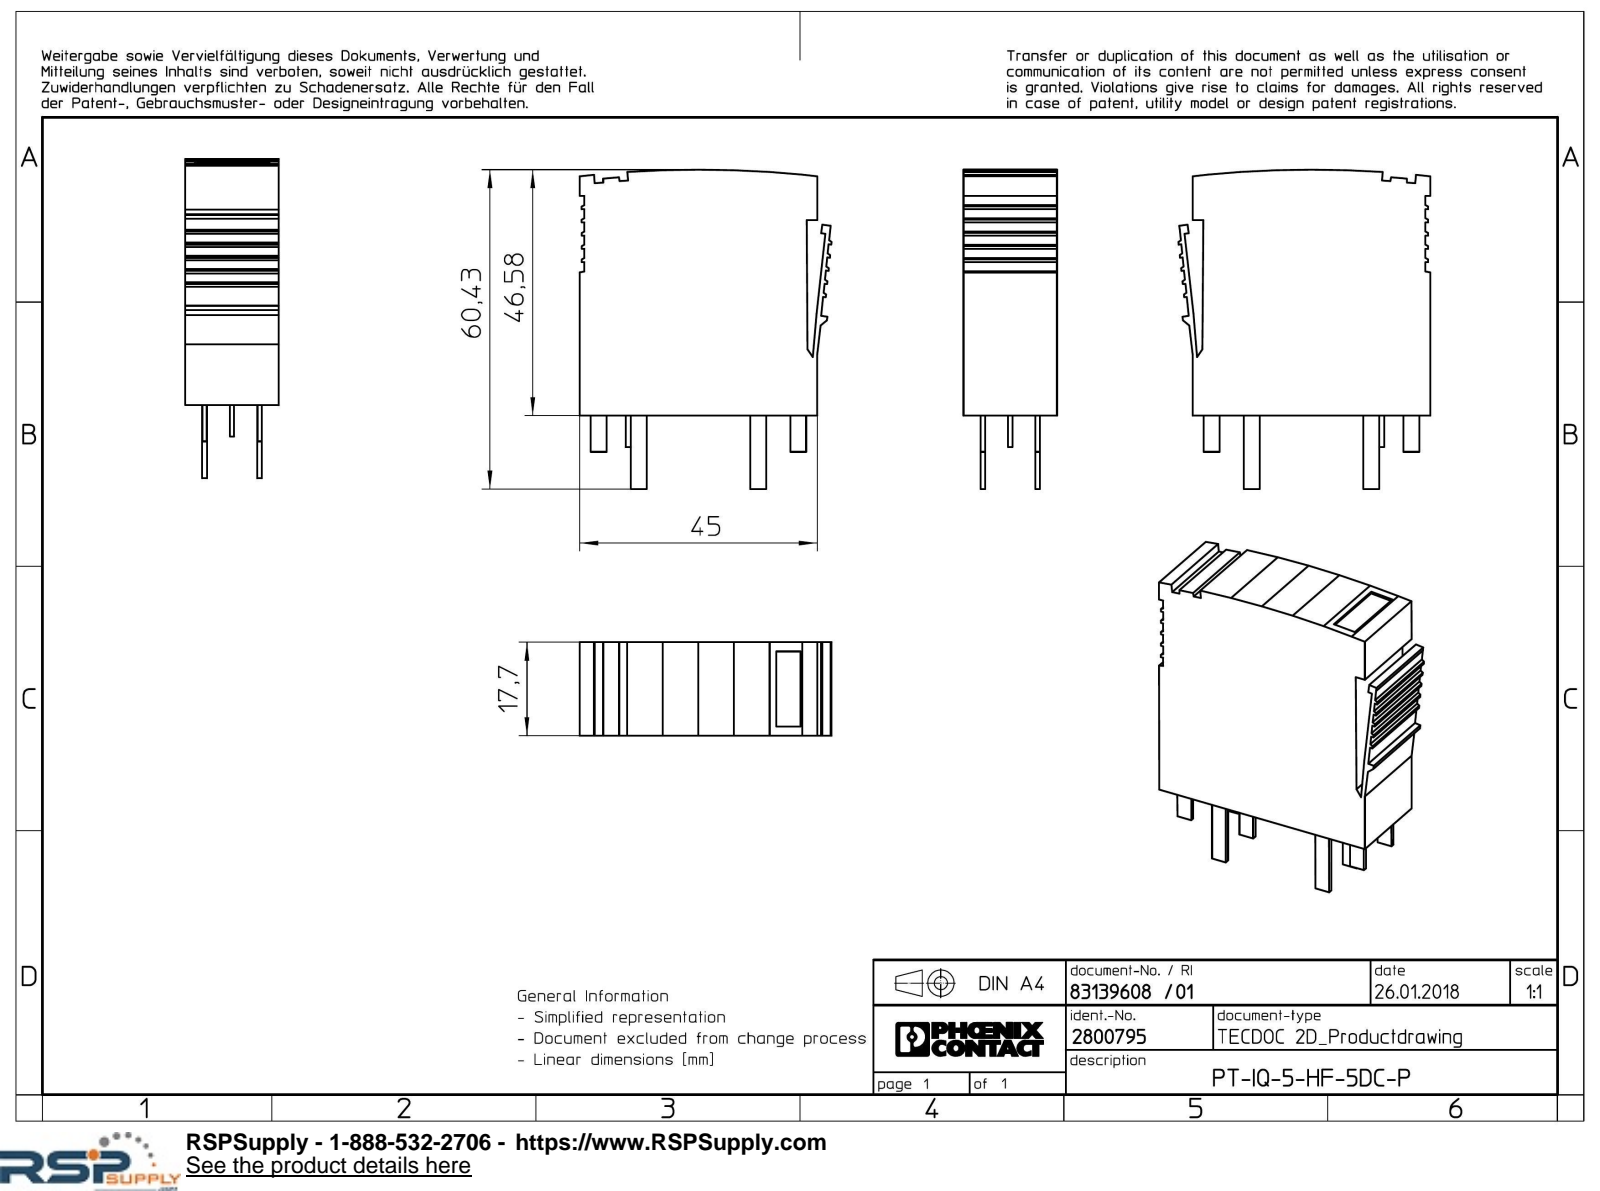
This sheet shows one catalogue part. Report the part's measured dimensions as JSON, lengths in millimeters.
{"part_name": "PT_IQ_5_HF...P-select", "step_written_by": "Creo Elements/Direct Modeling 20.1A 29-Sep-2018 (C) Parametric Technology GmbH (AUTOMOTIVE_DESIGN)", "units": "millimeters", "bodies": {"solids": 1, "faces": 174, "planar": 168, "cylindrical": 6, "other": 0}, "overall_size": [60.42, 47.71, 17.7], "volume_mm3": 35187, "surface_area_mm2": 9841, "partial_cylinders_radius": [[0.3, 4], [1.48, 2]], "face_to_face_distances": [17.7, 45, 0.9, 10.4, 44.1, 1.85, 3.2, 14.5, 4.1, 13.6]}
